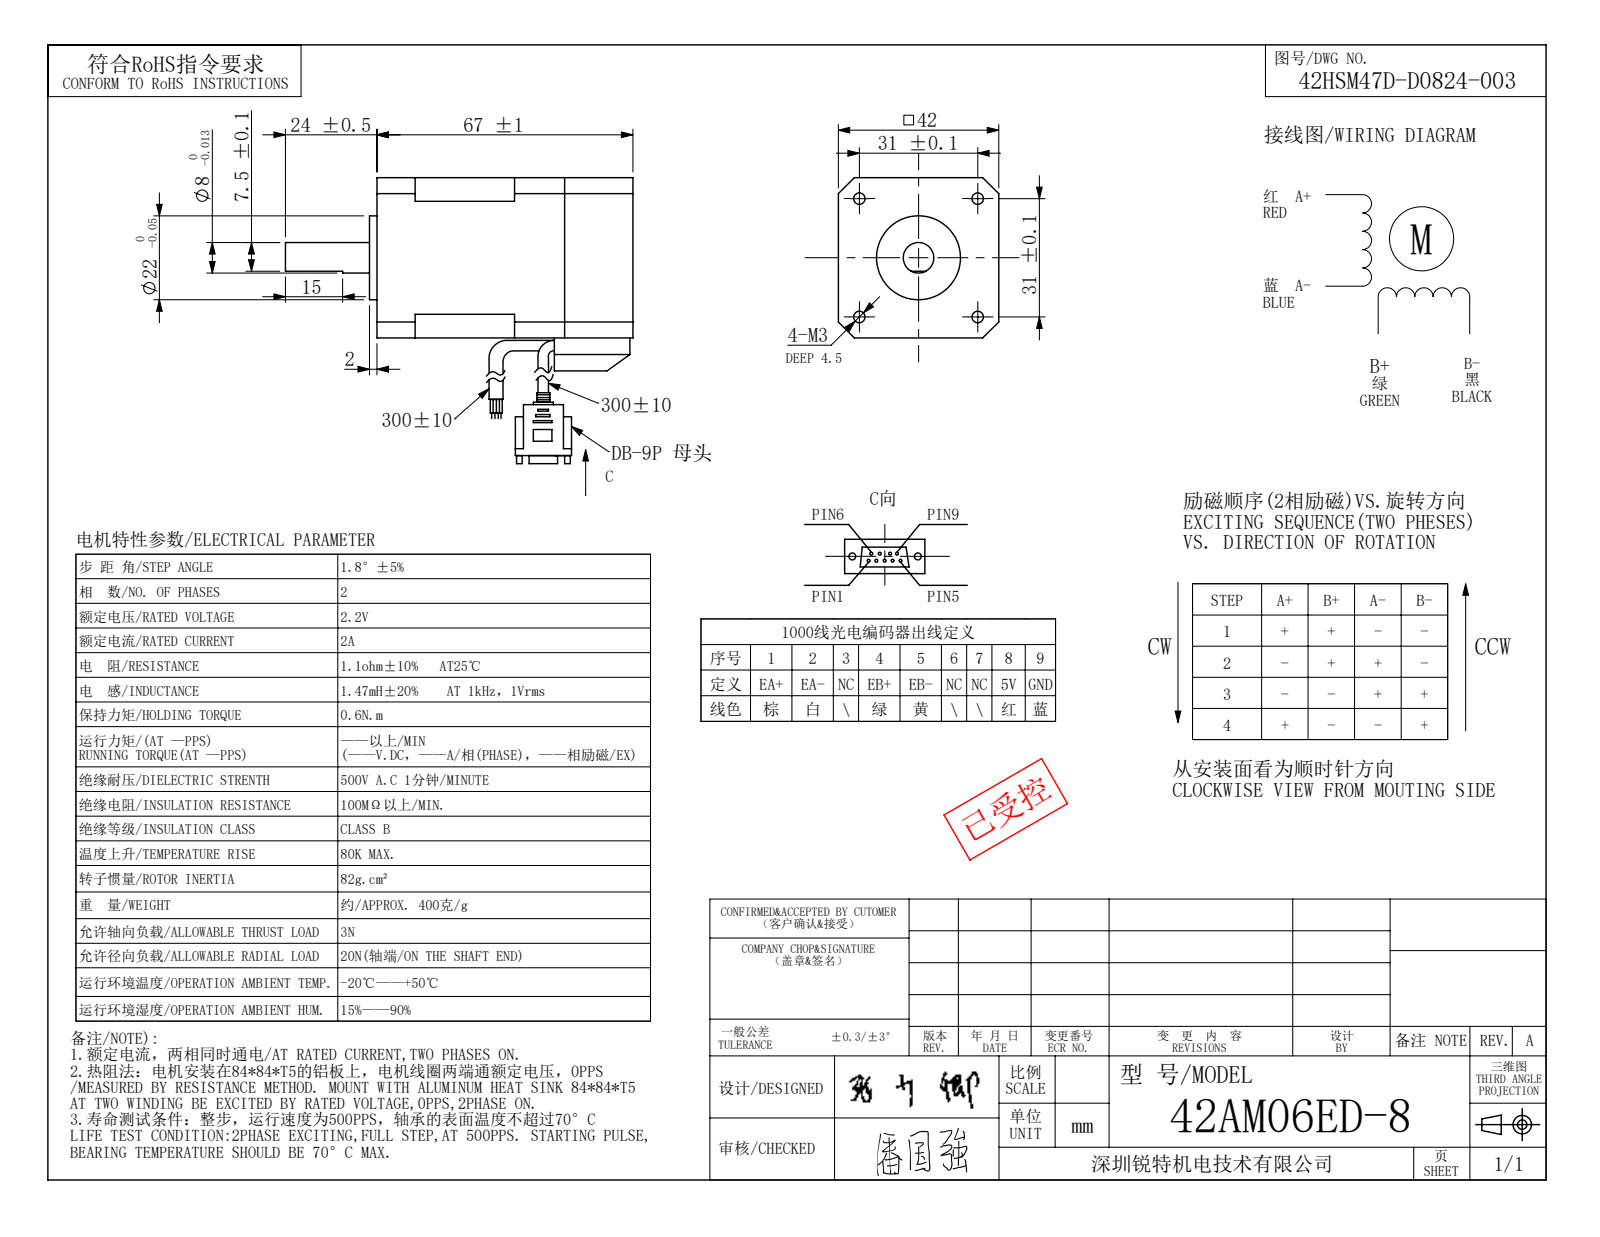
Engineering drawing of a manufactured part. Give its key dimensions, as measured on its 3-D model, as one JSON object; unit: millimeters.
{"step_written_by": "SolidWorks 2014 (AUTOMOTIVE_DESIGN)", "units": "millimeters", "bodies": {"solids": 1, "faces": 46, "planar": 34, "cylindrical": 12, "other": 0}, "overall_size": [91, 42, 42], "volume_mm3": 115266, "surface_area_mm2": 16468, "round_holes": [[3, 4]], "round_bosses_or_shafts": [[22, 1], [8, 1]], "face_to_face_distances": [42, 67, 1.41, 52.03, 50.62, 69, 2, 53.44, 53.45, 52.04], "hole_center_spacings": [31, 43.84]}
